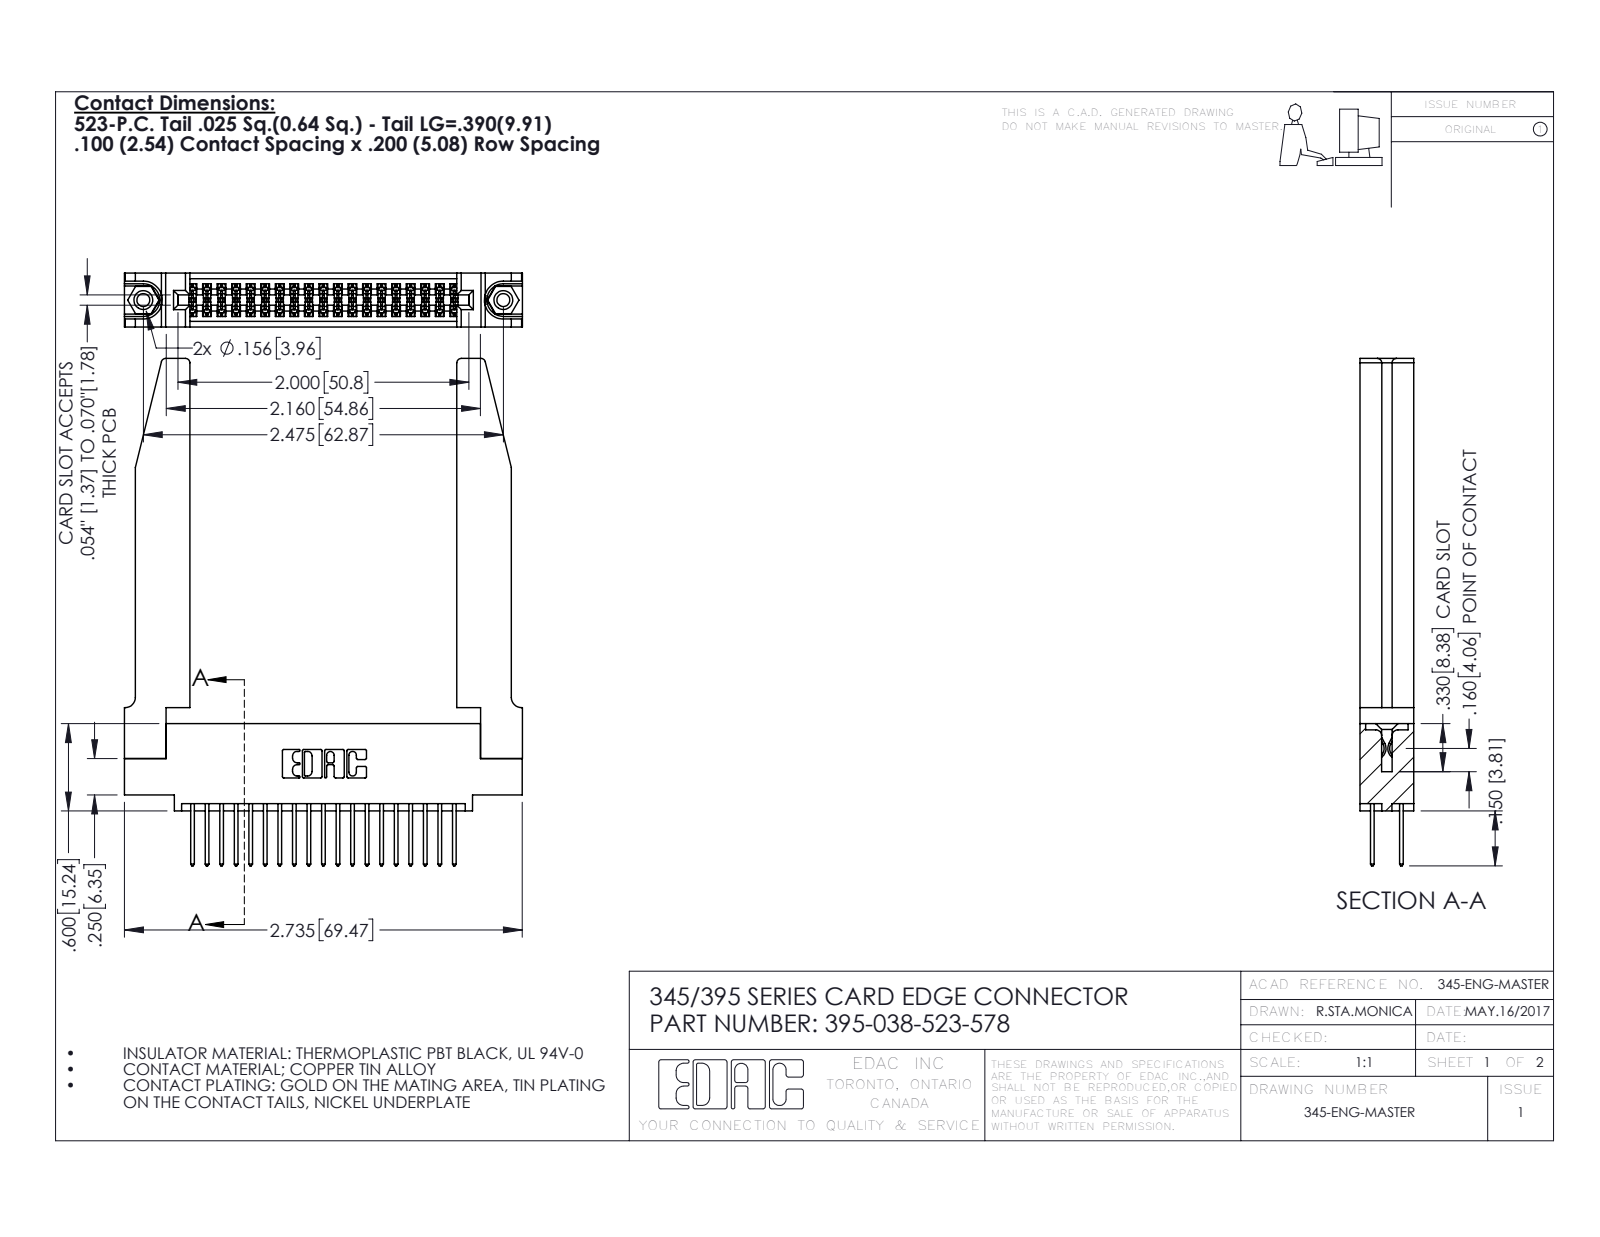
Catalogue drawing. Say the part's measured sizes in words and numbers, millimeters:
The part is named "395-038-523-578; 345-220-078_345-220-078; 345-250-001_345-250-001-102; 345-292-001_345-293-123 (+1 more)". Its 3-D file was written by "SolidWorks 2016 (CONFIG_CONTROL_DESIGN)". It is 43 solids with 2264 faces: 1480 planar, 732 cylindrical and 52 other. Overall it measures 88.6 by 69.5 by 9.4 millimeters. Its volume is 14 300 cubic millimeters and its surface area 16 500 square millimeters. Round holes: 2 of diameter 2.3, 2 of diameter 3.2, 2 of diameter 4, 1 of diameter 1.6. Round bosses or shafts: 2 of diameter 3.9. Partial cylindrical surfaces (rounded edges, fillets, slot ends): 57 of radius 0.2, 38 of radius 0.3, 22 of radius 0.3, 8 of radius 0.8, 6 of radius 0.2, 6 of radius 0.8, 3 of radius 0.7, 2 of radius 0.4. The main face-to-face distances are 9.4, 1.8, 7.6, 5.1, 2.5, 6.9, 0.6, 5.7, 3.8, 3.8. The hole center spacings are 6.9, 56.9, 62.9.
